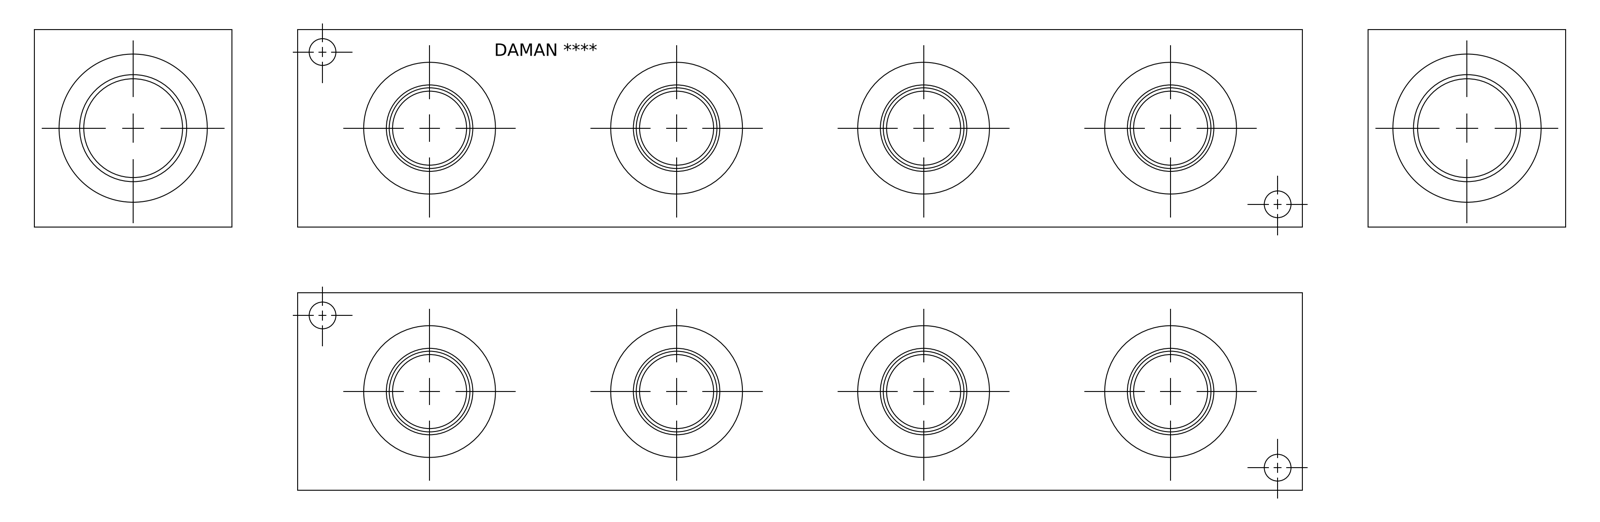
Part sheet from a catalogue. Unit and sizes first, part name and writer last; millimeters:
Units: millimetres
Overall size (bounding box): 387.35 × 76.2 × 76.2
Round holes (diameter × count): ⌀31.27 ×8, ⌀33.76 ×8, ⌀49.12 ×8, ⌀33.35 ×7, ⌀35.51 ×7, ⌀10.31 ×4, ⌀28.57 ×4, ⌀33.34 ×1, ⌀38.1 ×1, ⌀39.22 ×1, ⌀41.27 ×1, ⌀41.28 ×1
Main face-to-face distances: 76.2, 0.79, 75.41, 387.35, 386.56, 385.77, 19.84, 19.05, 56.36, 367.51
Hole centre spacings: 95.25, 50.65, 139.64, 233.62, 328.34, 190.5, 190.51, 372.94
Volume: 1 922 000 mm³ · Surface area: 169 475 mm²
Bodies: 1 solid, 455 faces (239 planar, 61 cylindrical, 155 other)
Part name (STEP PRODUCT): Part_AH0900416S_3D
STEP written by: Autodesk Inventor 2019 (AUTOMOTIVE_DESIGN)
